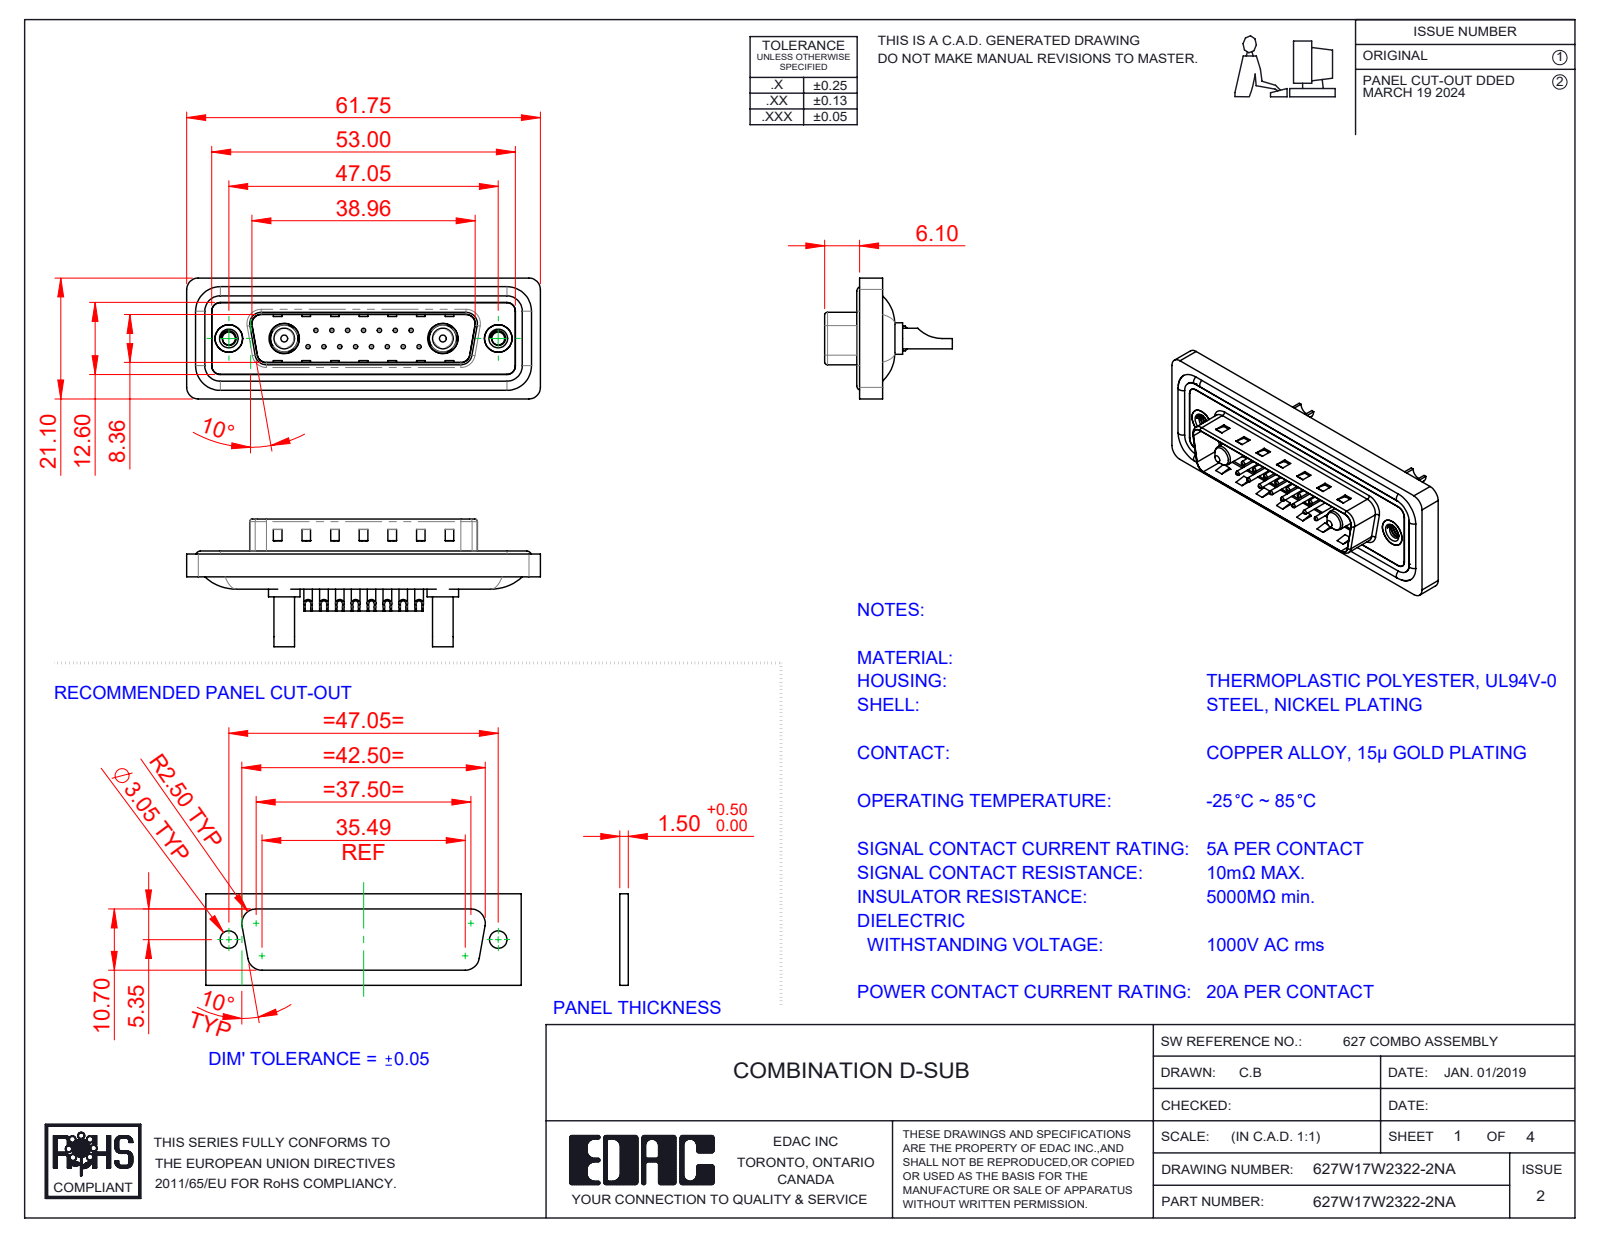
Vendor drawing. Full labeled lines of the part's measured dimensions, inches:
Part name (STEP PRODUCT): 627Combo Contact Row 2_22; 627W17W2322-2NA; 627Combo Housing_17W2; 627Combo Waterproof Housing_25 Contacts (+5 more)
STEP written by: SolidWorks 2023 (CONFIG_CONTROL_DESIGN)
Units: inches
Bodies: 26 solids, 1128 faces (370 planar, 474 cylindrical, 284 other)
Overall size (bounding box): 2.431 × 0.878 × 0.831
Volume: 0.447 in³ · Surface area: 18.9 in²
Round holes (diameter × count): ⌀0.03 ×15, ⌀0.039 ×15, ⌀0.063 ×15, ⌀0.079 ×15, ⌀0.089 ×2, ⌀0.106 ×2, ⌀0.157 ×2, ⌀0.189 ×2, ⌀0.191 ×2, ⌀0.197 ×2, ⌀0.209 ×2
Round bosses / shafts (diameter × count): ⌀0.059 ×15, ⌀0.063 ×4, ⌀0.217 ×2, ⌀0.205 ×2, ⌀0.193 ×2, ⌀0.187 ×2, ⌀0.148 ×2, ⌀0.142 ×2
Partial cylindrical surfaces — rounded edges, fillets, slot ends (radius × count): R0.059 ×22, R0.079 ×18, R0.02 ×8, R0.063 ×8, R0.039 ×6, R0.01 ×4, R0.024 ×4, R0.026 ×4
Main face-to-face distances: 0.016, 0.059, 0.043, 0.063, 0.02, 0.122, 0.114, 0.032, 0.377, 0.161
Hole centre spacings: 0.124, 0.109, 0.218, 0.327, 0.198, 0.295, 0.436, 0.198
